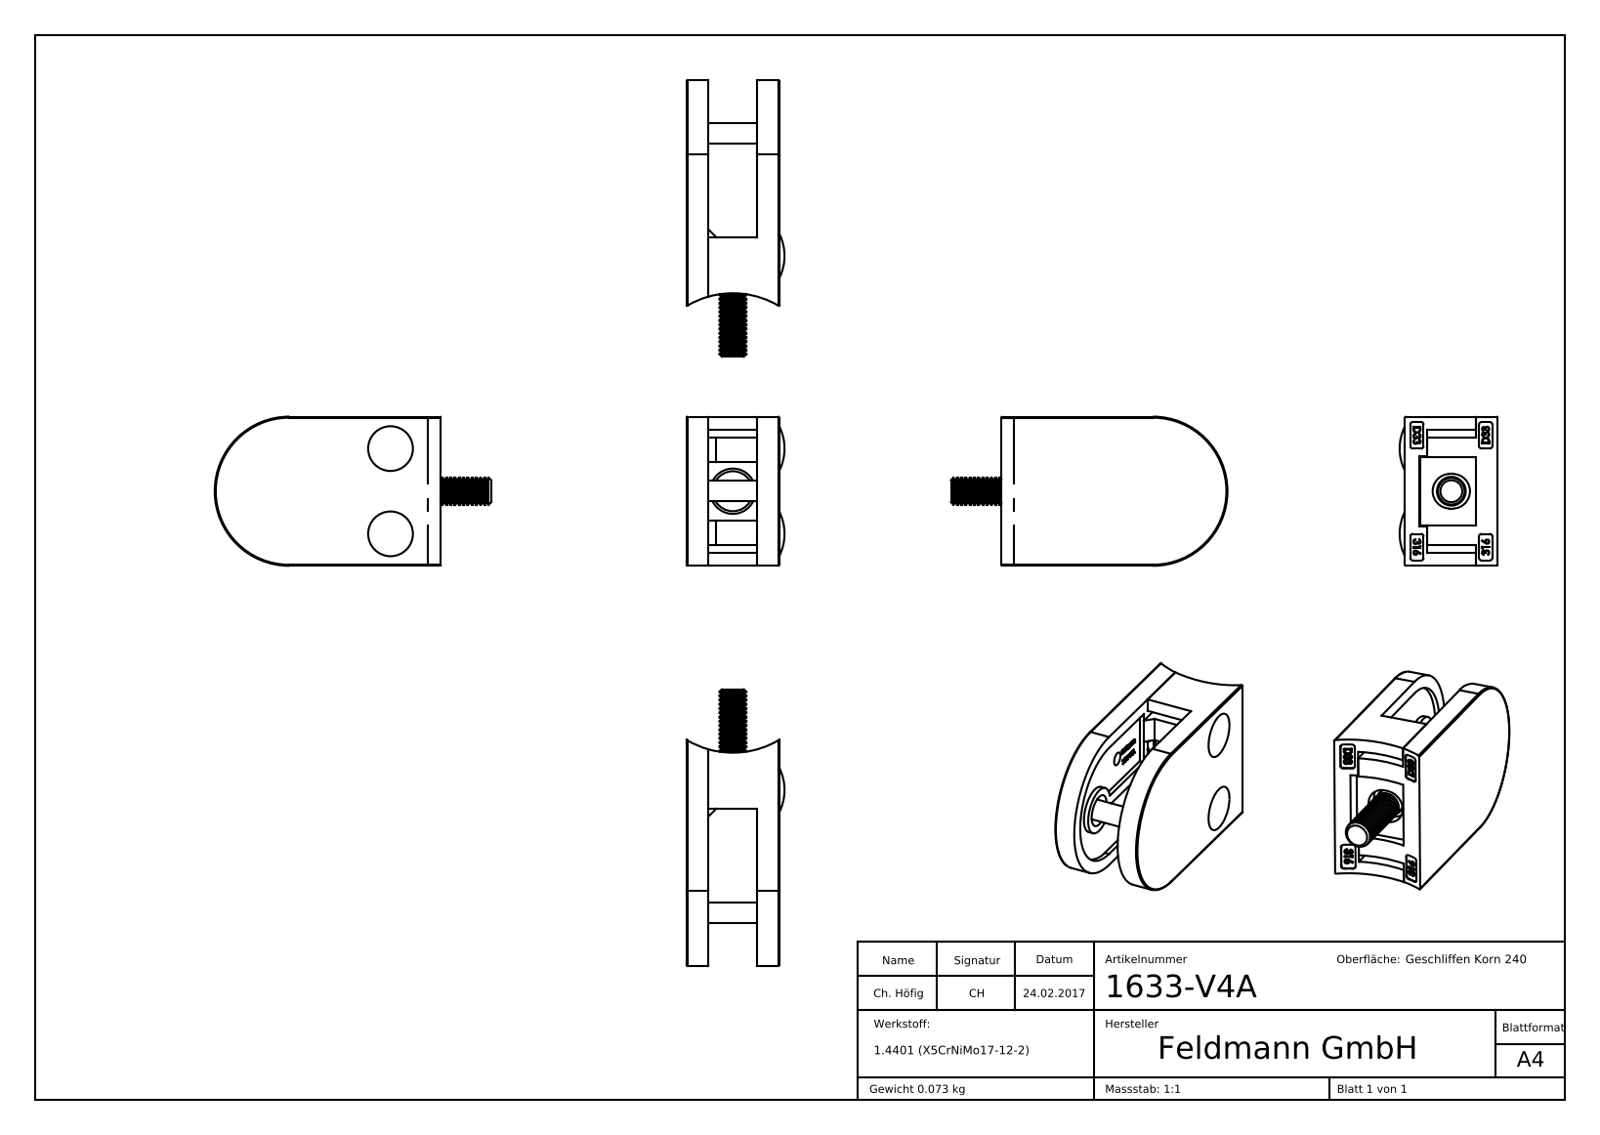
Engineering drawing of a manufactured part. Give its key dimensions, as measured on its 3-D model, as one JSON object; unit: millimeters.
{"part_name": "socket countersunk head screw_din_DIN 7991 - M4 x 10 --- 10S; 16-Stift_16-Stift; 16xx-XXX Teil2_1633-V4A; 16xx-XXX Teil1_1633-V4A (+3 more)", "step_written_by": "SolidWorks 2015 (CONFIG_CONTROL_DESIGN)", "units": "millimeters", "bodies": {"solids": 8, "faces": 1423, "planar": 624, "cylindrical": 202, "other": 597}, "overall_size": [51.9, 28, 18.4], "volume_mm3": 9843, "surface_area_mm2": 9072, "round_holes": [[1, 2], [2.5, 2], [3.3, 2], [4.15, 2], [8.2, 2], [3.9, 1], [6, 1]], "round_bosses_or_shafts": [[7.64, 2], [4, 2], [2.5, 2], [8.8, 1], [8.5, 1], [5, 1], [3.85, 1]], "partial_cylinders_radius": [[0.5, 20], [0.2, 4], [3.25, 2], [11.6, 1], [14, 1], [16.85, 1], [16.95, 1]], "face_to_face_distances": [17.4, 4.1, 13.3, 3.2, 14.2, 0.9, 10.1, 11, 9.2, 2.5], "hole_center_spacings": [10.99, 14.1, 20.01, 24.35, 12.6, 16]}
